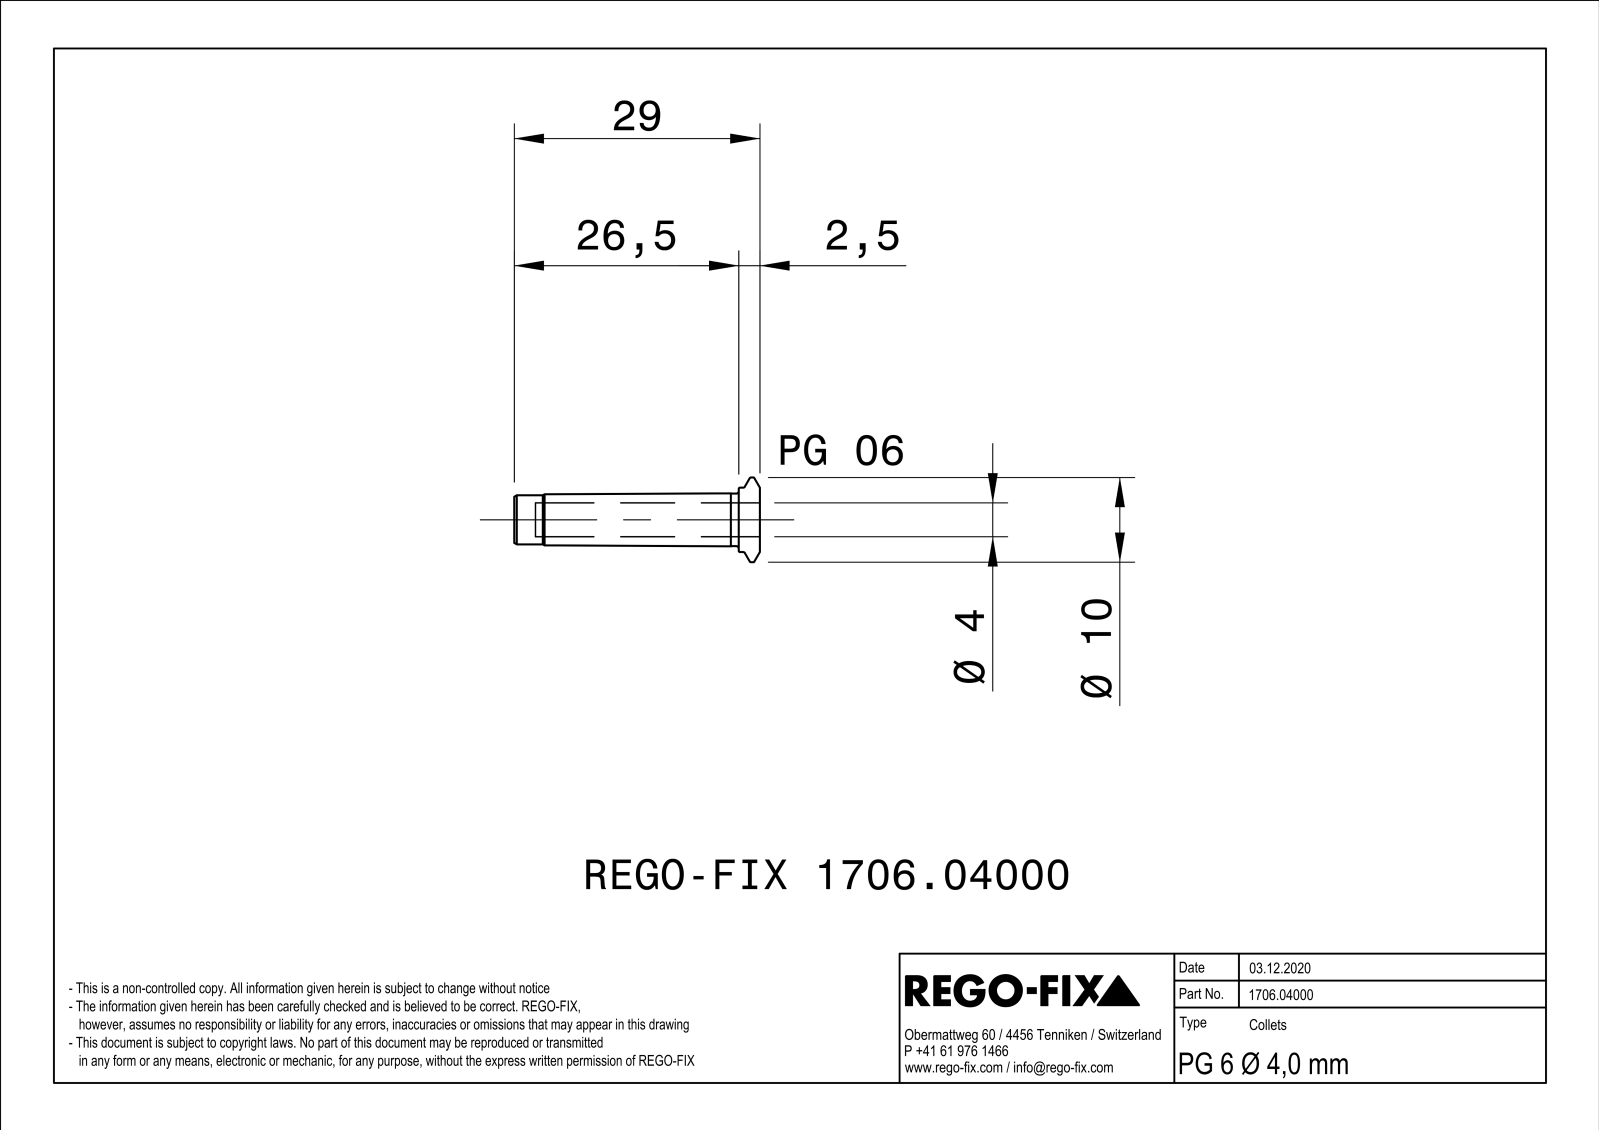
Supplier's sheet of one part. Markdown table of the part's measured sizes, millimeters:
| quantity | value |
| --- | --- |
| part name | NOCUT |
| STEP written by | SIEMENS PLM Software Solid Edge ST10 (AUTOMOTIVE_DESIGN) |
| units | millimeters |
| bodies | 1 solid, 59 faces (17 planar, 11 cylindrical, 31 other) |
| overall size | 29 × 10 × 9.99 |
| volume | 533 mm³ |
| surface area | 1 118 mm² |
| round holes (diameter × count) | 4 × 1 |
| round bosses / shafts (diameter × count) | 10 × 1, 7.6 × 1, 6.2 × 1, 5.8 × 1 |
| main face-to-face distances | 0.45, 0.46, 29, 2.5, 26.5 |
